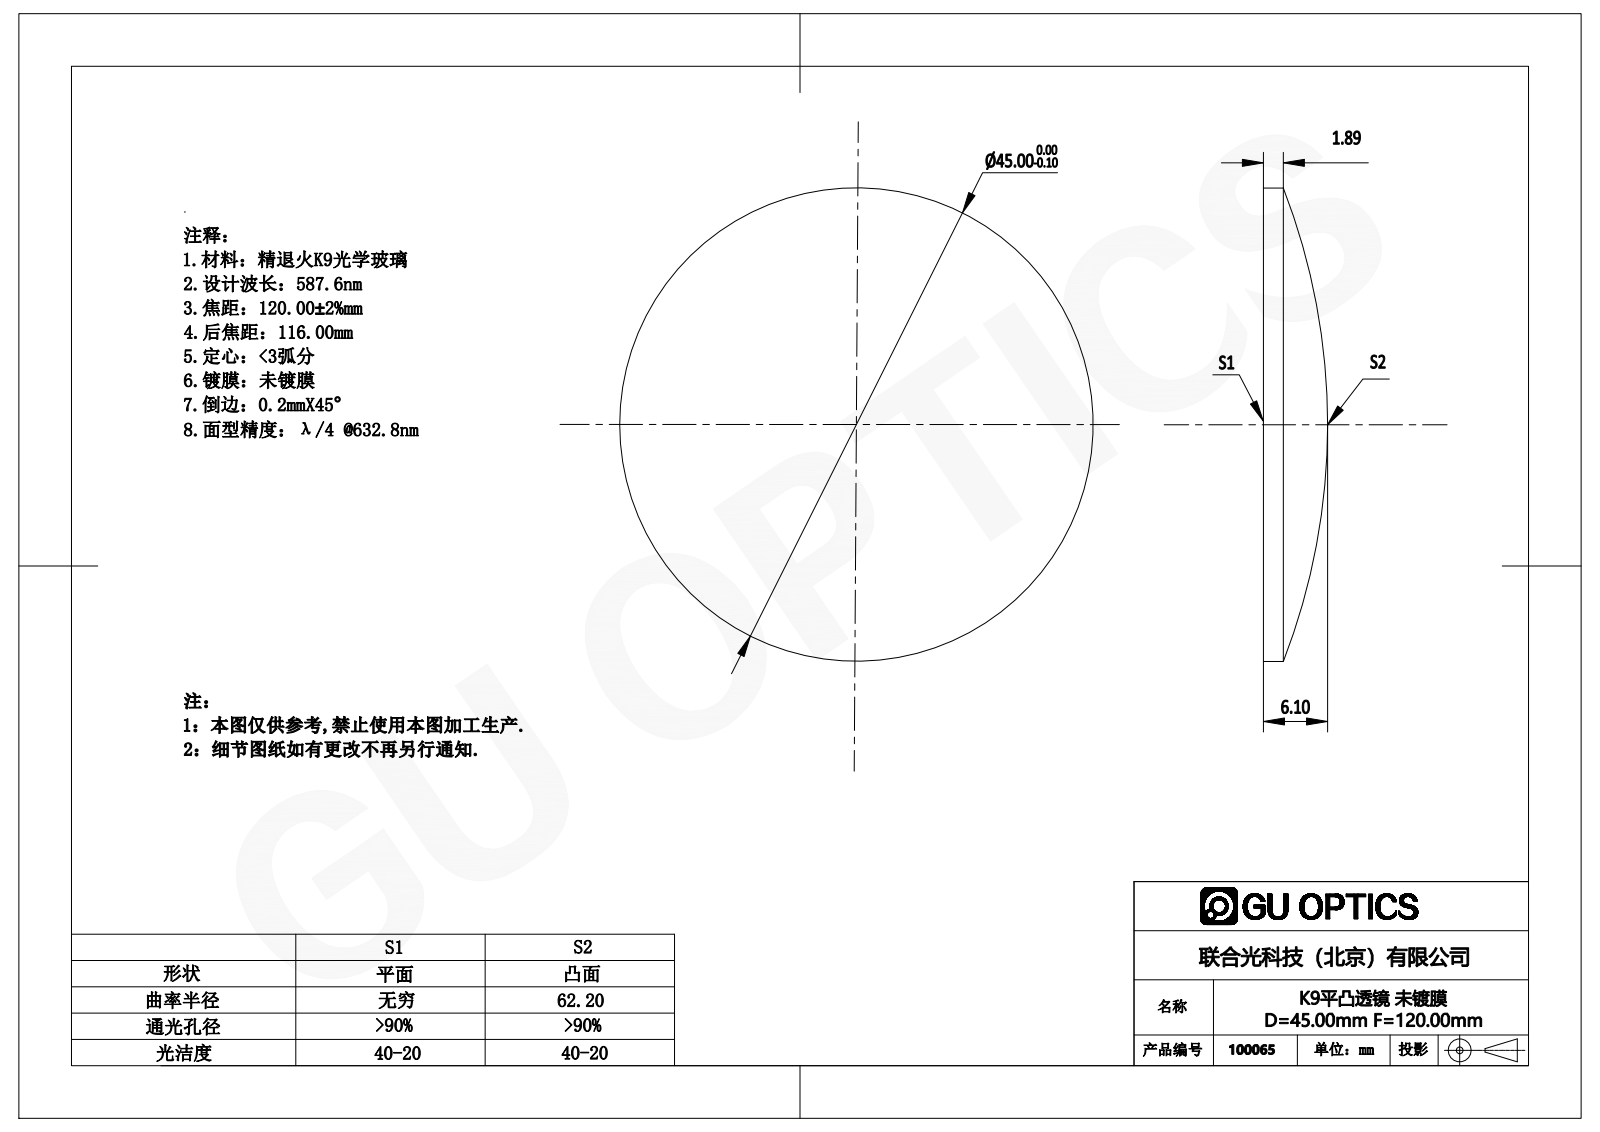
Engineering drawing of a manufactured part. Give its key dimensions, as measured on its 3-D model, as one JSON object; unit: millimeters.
{"part_name": "100065", "step_written_by": "SolidWorks 2016 (AUTOMOTIVE_DESIGN)", "units": "millimeters", "bodies": {"solids": 1, "faces": 5, "planar": 1, "cylindrical": 2, "other": 2}, "overall_size": [45, 45, 6.1], "volume_mm3": 6393, "surface_area_mm2": 3504, "round_bosses_or_shafts": [[45, 1]]}
